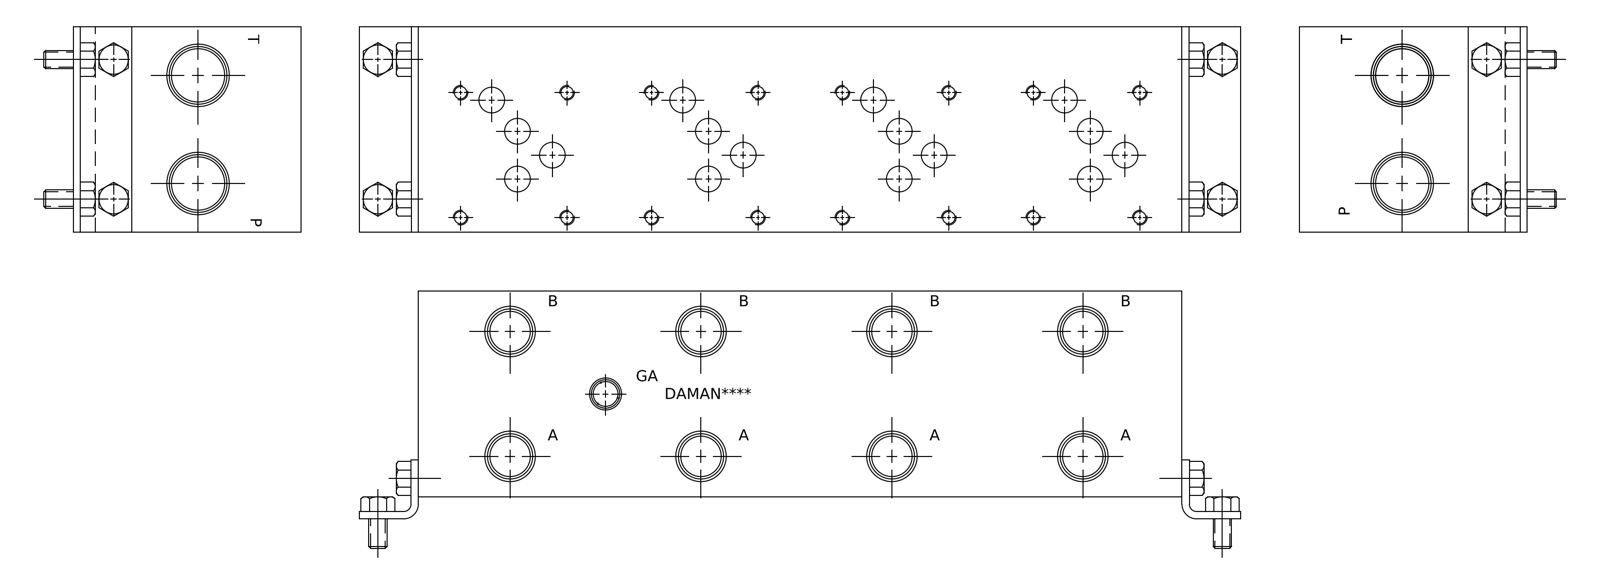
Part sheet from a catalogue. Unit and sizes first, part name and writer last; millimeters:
Units: millimetres
Overall size (bounding box): 330.2 × 88.9 × 88.9
Round holes (diameter × count): ⌀5.11 ×16, ⌀6.35 ×16, ⌀11.13 ×16, ⌀17.48 ×8, ⌀21.59 ×8, ⌀6.53 ×2, ⌀7.92 ×2, ⌀23.01 ×2, ⌀26.92 ×2, ⌀10.72 ×1, ⌀13.87 ×1
Main face-to-face distances: 88.9, 330.2, 15.37, 73.53, 15.85, 314.35, 298.5, 15.33, 88.86, 69.85
Hole centre spacings: 82.55, 165.1, 98.63, 70.95, 18.27, 46.05, 53.98, 68.25
Volume: 2 497 000 mm³ · Surface area: 159 234 mm²
Bodies: 1 solid, 726 faces (421 planar, 82 cylindrical, 223 other)
Part name (STEP PRODUCT): Part_AD05P043P_3D
STEP written by: Autodesk Inventor 2020 (AUTOMOTIVE_DESIGN)
